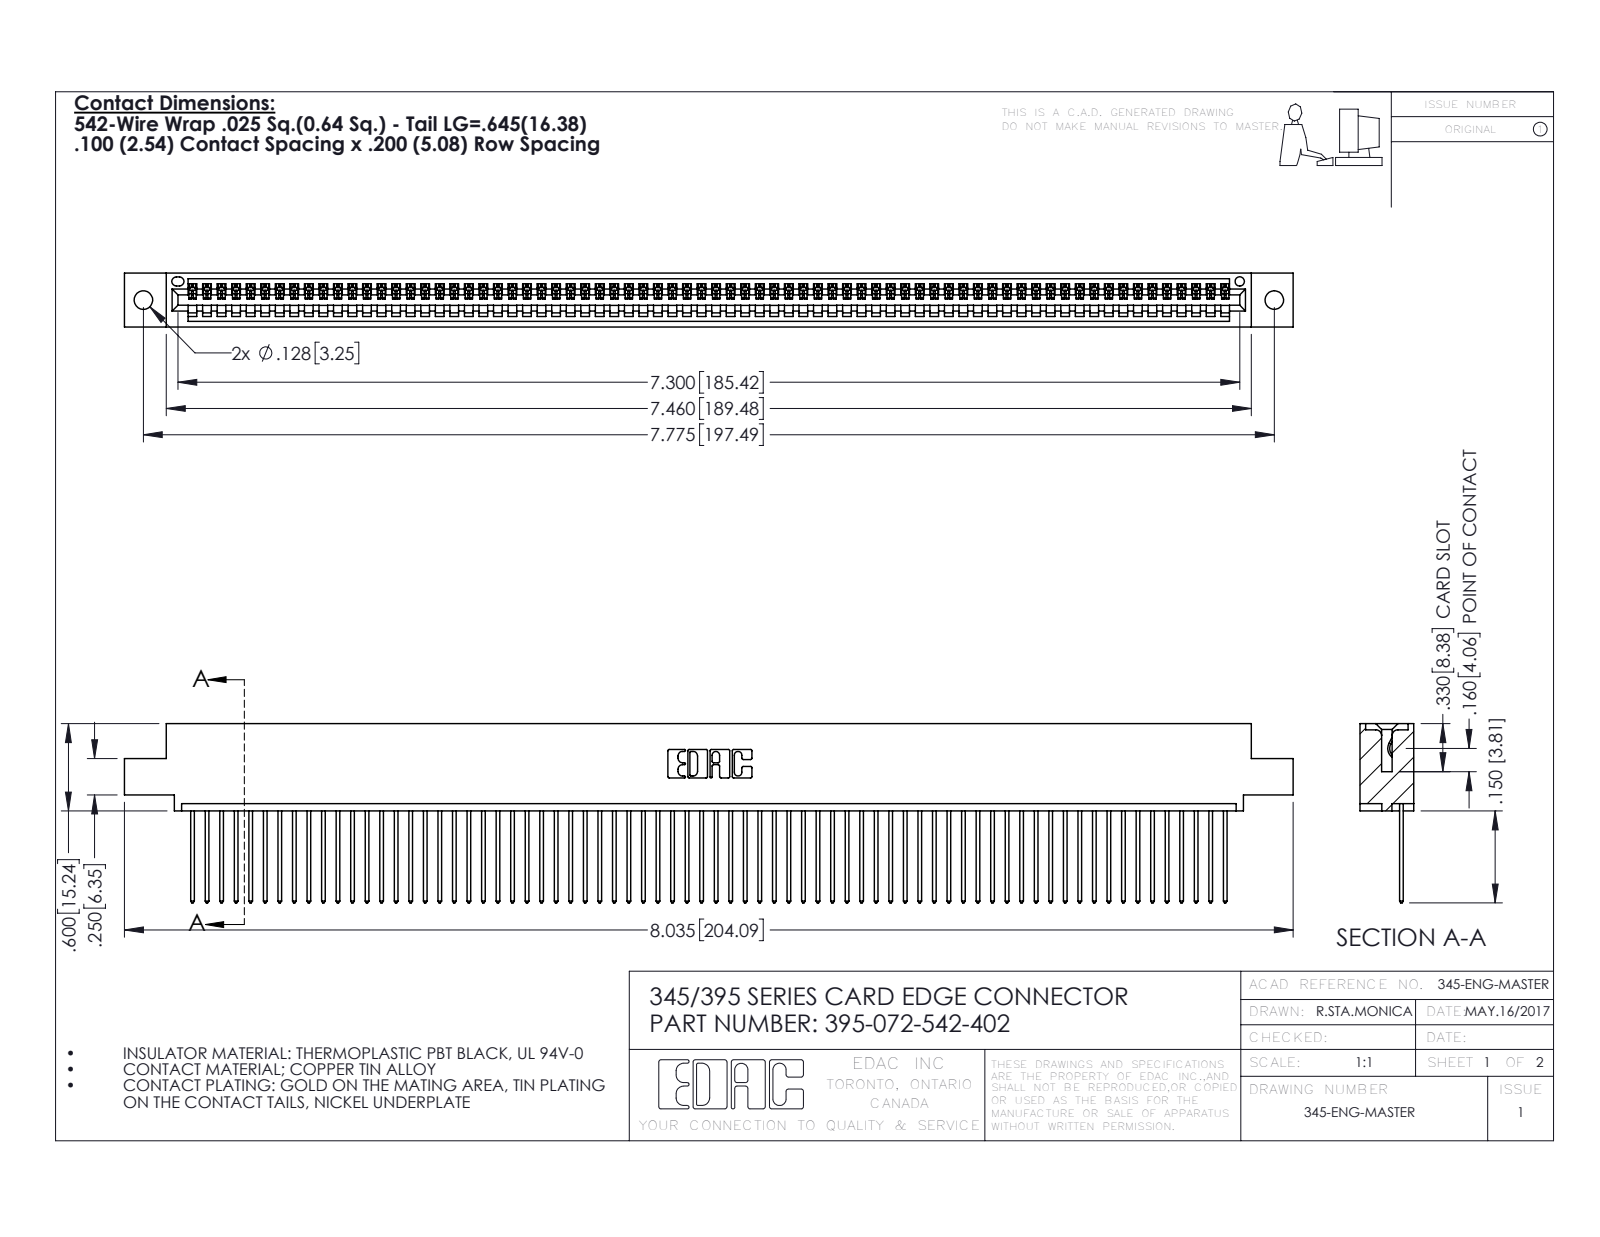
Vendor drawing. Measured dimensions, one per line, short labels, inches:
name: 345 Part_0.110 Offset - 0.128 Dia; 345-292-001_345-293-142; 395-072-542-402
written by: SolidWorks 2016 (CONFIG_CONTROL_DESIGN)
unit: in
bodies: 73 solids, 4306 faces (2964 planar, 1342 cylindrical, 0 other)
size: 8.035 × 1.232 × 0.37
volume: 1.201 in³; area: 42.45 in²
holes: 2× ⌀0.128, 1× ⌀0.064
rounds: 144× R0.006, 144× R0.01, 22× R0.01, 6× R0.007, 6× R0.031, 3× R0.026, 2× R0.031, 2× R0.04
face distances: 0.072, 0.298, 0.098, 0.272, 0.025, 0.37, 0.2, 0.225, 0.149, 0.072
hole spacings: 0.27, 7.539, 7.775
